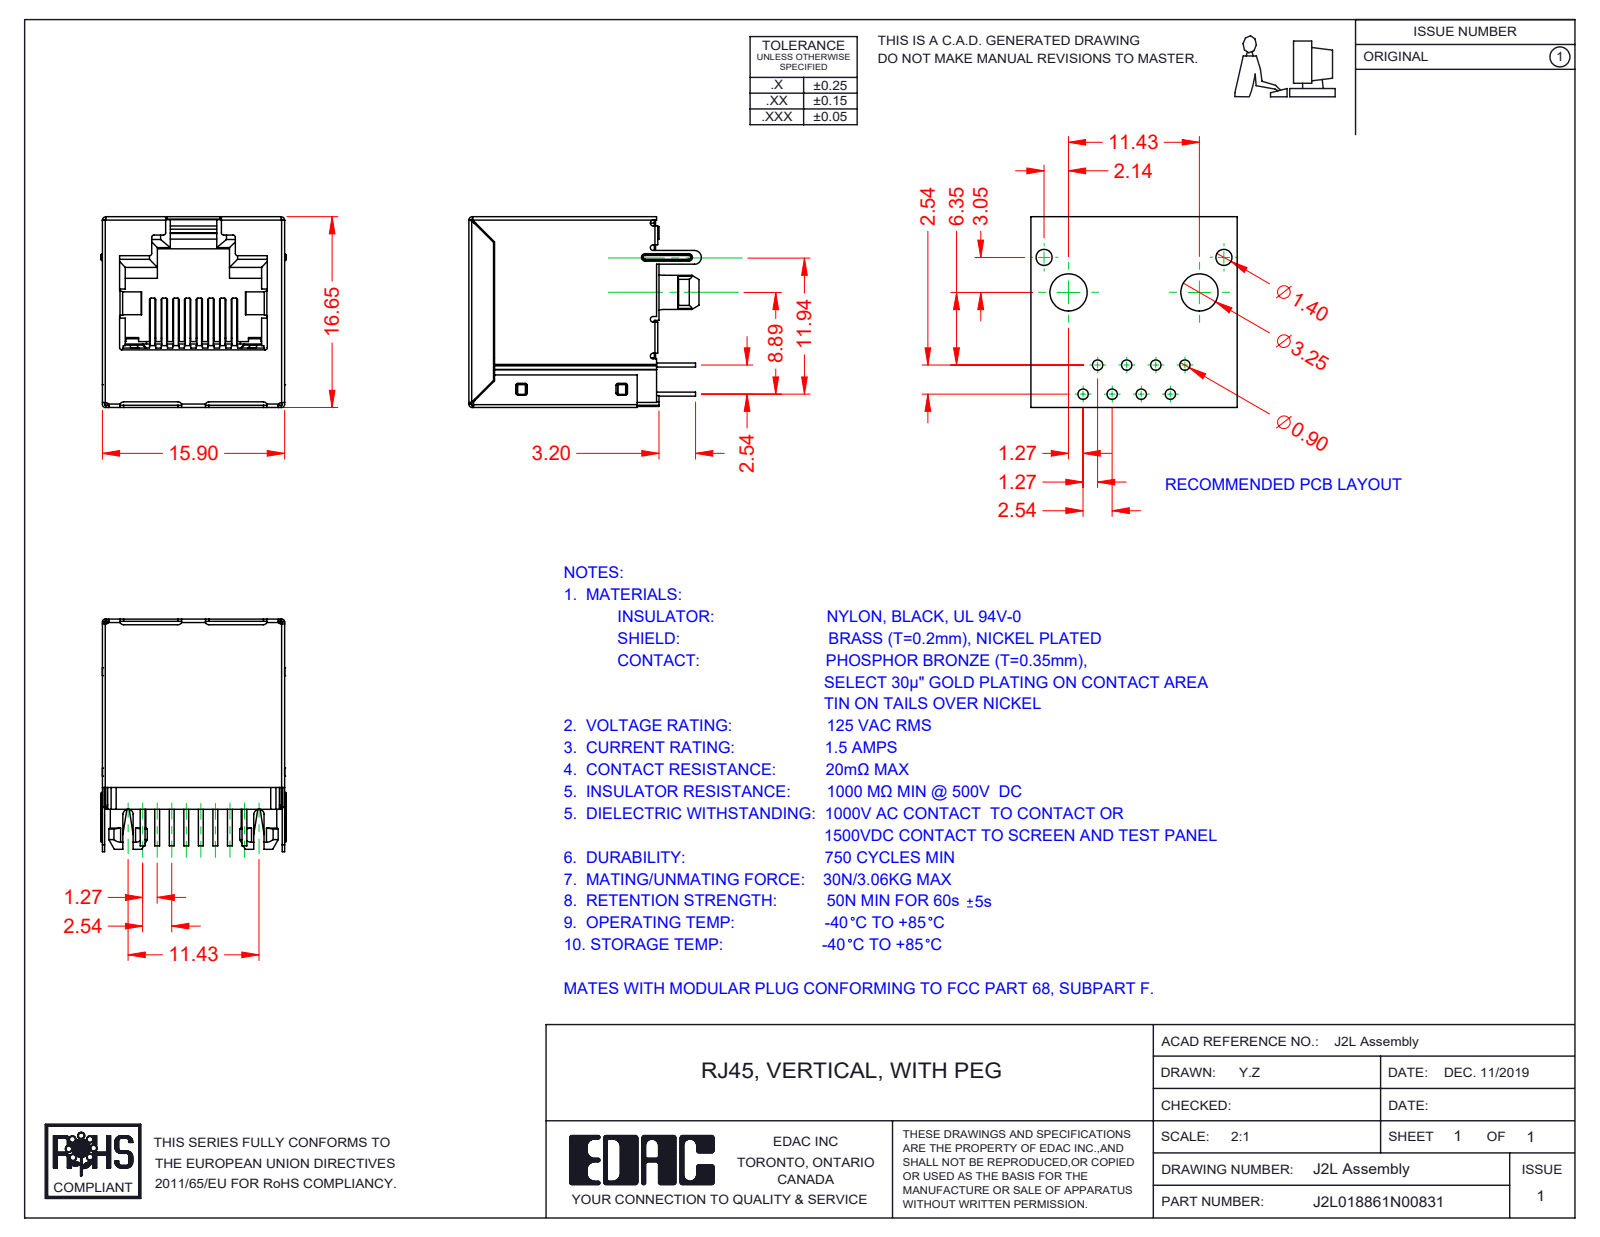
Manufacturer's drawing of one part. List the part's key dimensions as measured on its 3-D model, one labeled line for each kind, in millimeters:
Part name (STEP PRODUCT): 2L Contacts; 2L Contact Lock; 2L Shield; 2L Insulator (+2 more)
STEP written by: SolidWorks 2016 (CONFIG_CONTROL_DESIGN)
Units: millimetres
Bodies: 12 solids, 1131 faces (784 planar, 284 cylindrical, 63 other)
Overall size (bounding box): 20.3 × 16.65 × 16.2
Volume: 2 735 mm³ · Surface area: 6 843 mm²
Round bosses / shafts (diameter × count): ⌀3.1 ×2, ⌀1.1 ×2
Partial cylindrical surfaces — rounded edges, fillets, slot ends (radius × count): R0.15 ×64, R0.25 ×20, R0.2 ×16, R0.3 ×14, R0.35 ×9, R0.1 ×8, R0.28 ×4, R0.5 ×3
Main face-to-face distances: 15.45, 15.7, 16.45, 16.2, 16.4, 15.65, 16.3, 16.25, 15.9, 15.5
